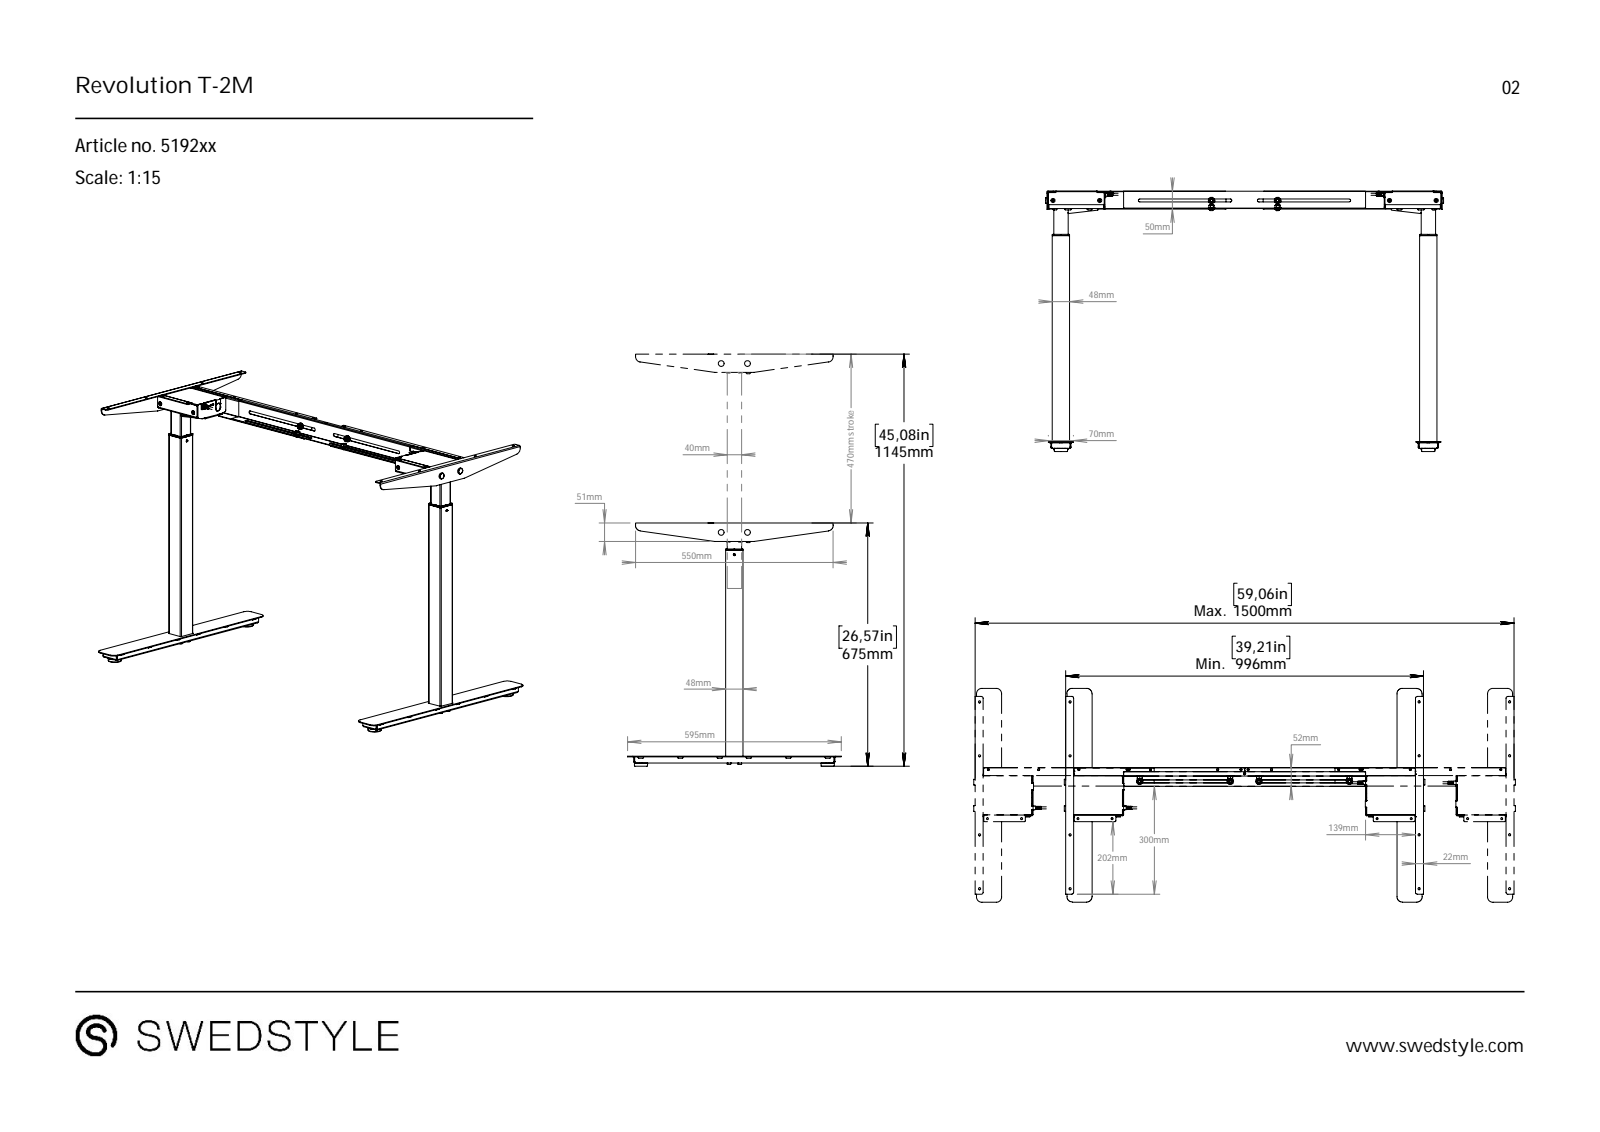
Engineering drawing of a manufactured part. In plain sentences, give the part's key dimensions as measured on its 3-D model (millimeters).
The part is named "Revolution T-2M, dummy_02_5192xx". Its 3-D file was written by "SolidWorks 2021 (CONFIG_CONTROL_DESIGN)". It is 0 solids with 1254 faces: 590 planar, 319 cylindrical and 345 other. Overall it measures 1108.2 by 725.03 by 595 millimeters. Round holes: 8 of diameter 5.5, 8 of diameter 6, 6 of diameter 14, 3 of diameter 11.34, 2 of diameter 8, 2 of diameter 13, 1 of diameter 5.3. Round bosses or shafts: 8 of diameter 10, 2 of diameter 14, 2 of diameter 8.5, 2 of diameter 5.5, 1 of diameter 11.34. Partial cylindrical surfaces (rounded edges, fillets, slot ends): 32 of radius 0.5, 27 of radius 2.5, 18 of radius 2, 10 of radius 3.3, 10 of radius 15, 8 of radius 1, 5 of radius 4, 4 of radius 0.1. The main face-to-face distances are 4, 44, 48, 2, 1.5, 1023, 40, 32.5, 76.5, 1027. The hole center spacings are 47.98, 113.15, 150, 331.06, 370, 480.73, 1050.26, 1055.25.
